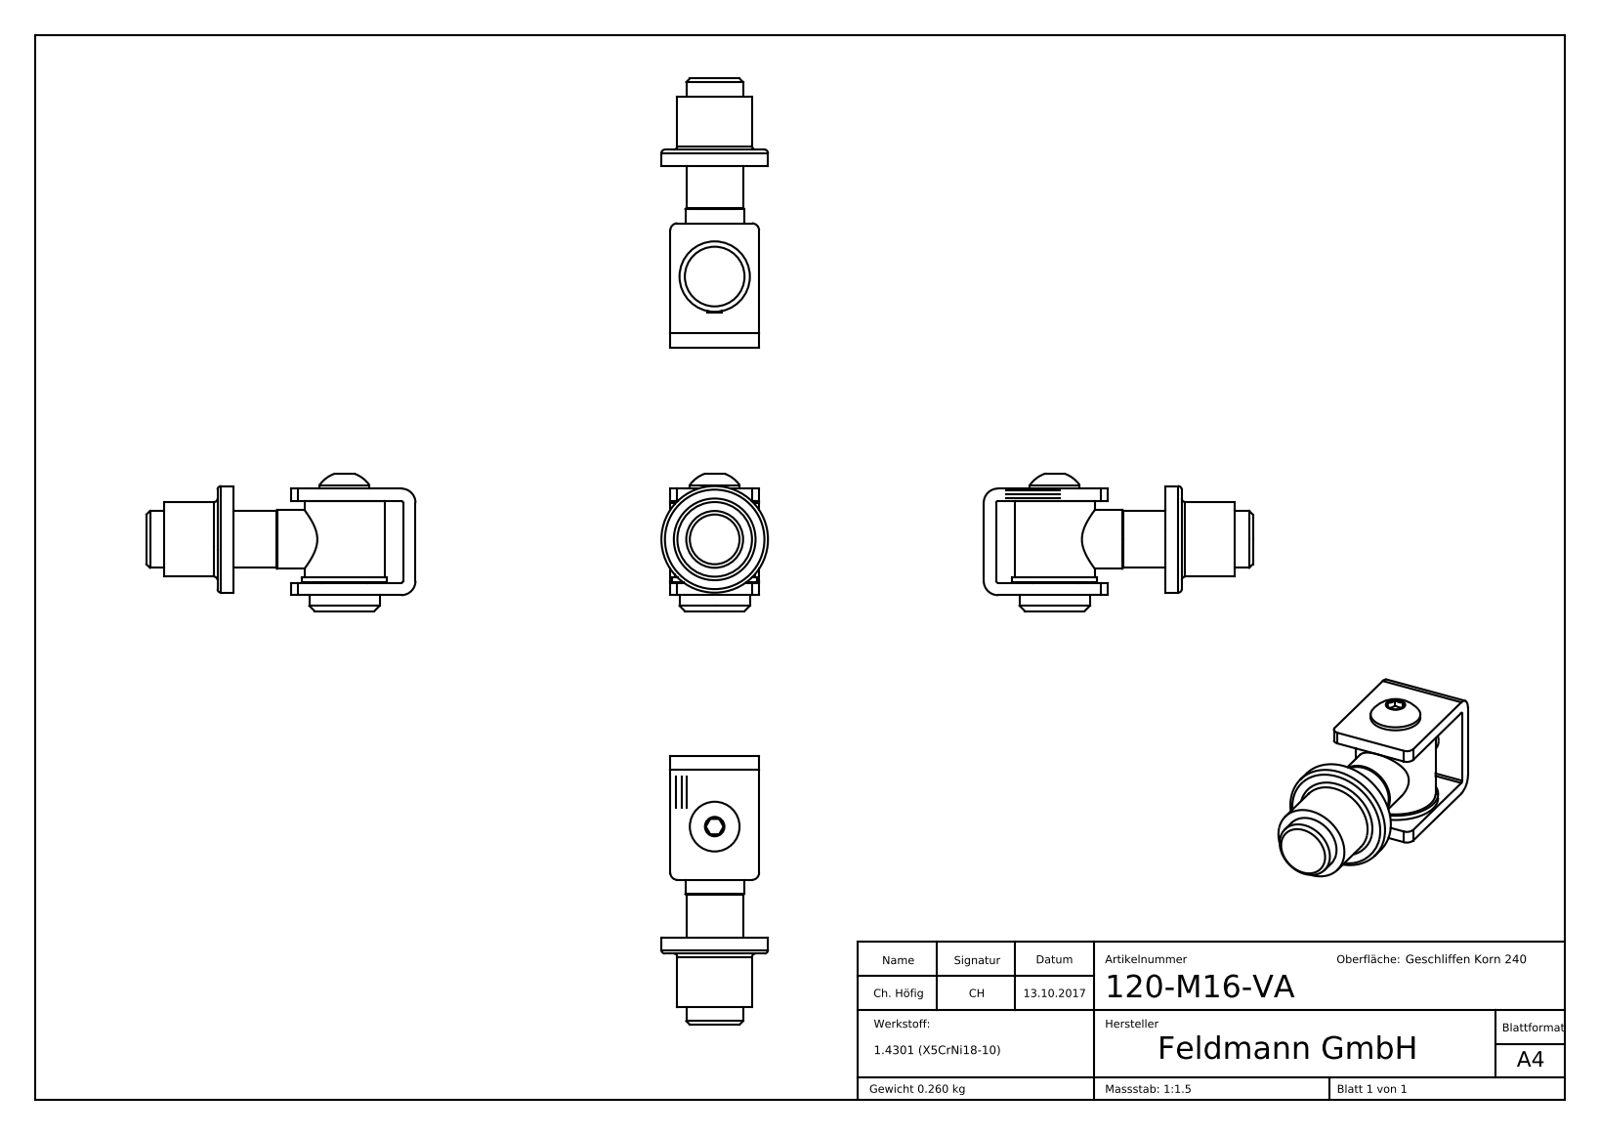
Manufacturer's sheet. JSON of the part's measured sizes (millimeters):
{"part_name": "120-M16-VA Teil5_120-M16-VA Teil5; 120-M16-VA; 120-M16-VA Teil4_120-M12-VA Teil 4; 120-M16-VA Teil3 (+8 more)", "step_written_by": "SolidWorks 2018 (CONFIG_CONTROL_DESIGN)", "units": "millimeters", "bodies": {"solids": 6, "faces": 293, "planar": 174, "cylindrical": 27, "other": 92}, "overall_size": [75.75, 38.7, 30], "volume_mm3": 32879, "surface_area_mm2": 17453, "round_holes": [[5, 1], [7.55, 1], [10, 1], [12.8, 1], [13, 1], [14, 1]], "round_bosses_or_shafts": [[30, 1], [24, 1], [22.5, 1], [21, 1], [19.8, 1], [16.5, 1], [16, 1], [14, 1]], "partial_cylinders_radius": [[0.5, 2], [2, 2], [4, 2]], "face_to_face_distances": [3.5, 26.5, 30, 23, 3.55, 4.95, 26.45, 1.45, 22.95, 21.55], "hole_center_spacings": [0.7]}
